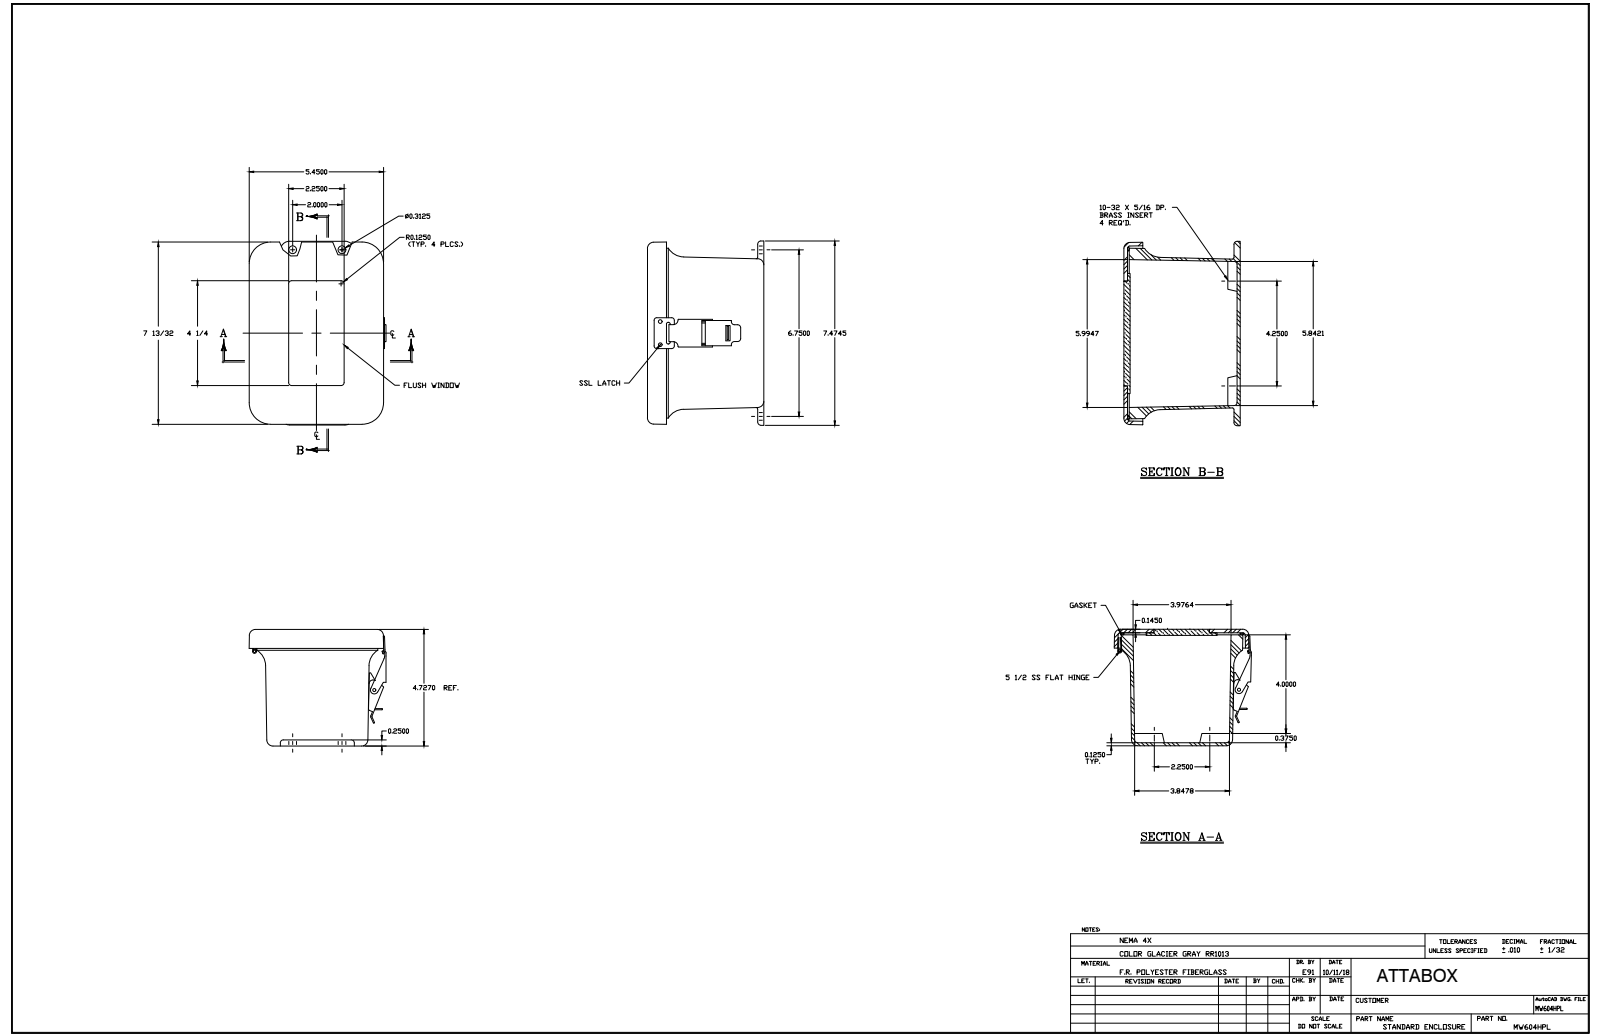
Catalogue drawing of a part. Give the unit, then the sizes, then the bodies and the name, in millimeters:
Units: millimetres
Overall size (bounding box): 189.8 × 142.7 × 119.5
Round holes (diameter × count): ⌀3.6 ×11, ⌀3.3 ×5, ⌀3.9 ×5, ⌀2.6 ×4, ⌀4 ×4, ⌀5.5 ×4, ⌀3.3 ×2, ⌀3.4 ×2, ⌀3.4 ×2, ⌀2.2 ×1, ⌀2.2 ×1, ⌀9.5 ×1
Round bosses / shafts (diameter × count): ⌀3.2 ×6, ⌀6.4 ×5, ⌀6.9 ×4, ⌀3.2 ×3, ⌀7.6 ×1, ⌀4.3 ×1, ⌀3.9 ×1, ⌀3.9 ×1
Partial cylindrical surfaces — rounded edges, fillets, slot ends (radius × count): R0.8 ×20, R3.2 ×20, R0.4 ×12, R6.4 ×12, R1.1 ×8, R0.8 ×6, R0.6 ×4, R1.5 ×4
Main face-to-face distances: 3.7, 115.8, 119.5, 6.4, 113.1, 3.2, 112.6, 116.3, 110, 2.7
Hole centre spacings: 23.8, 63.5, 84.8, 19.1, 11.9, 12.7, 34.1, 36.9
Volume: 541 900 mm³ · Surface area: 272 200 mm²
Bodies: 26 solids, 654 faces (264 planar, 266 cylindrical, 124 other)
Part name (STEP PRODUCT): MW604HPL
STEP written by: SolidWorks 2018 (AUTOMOTIVE_DESIGN)
